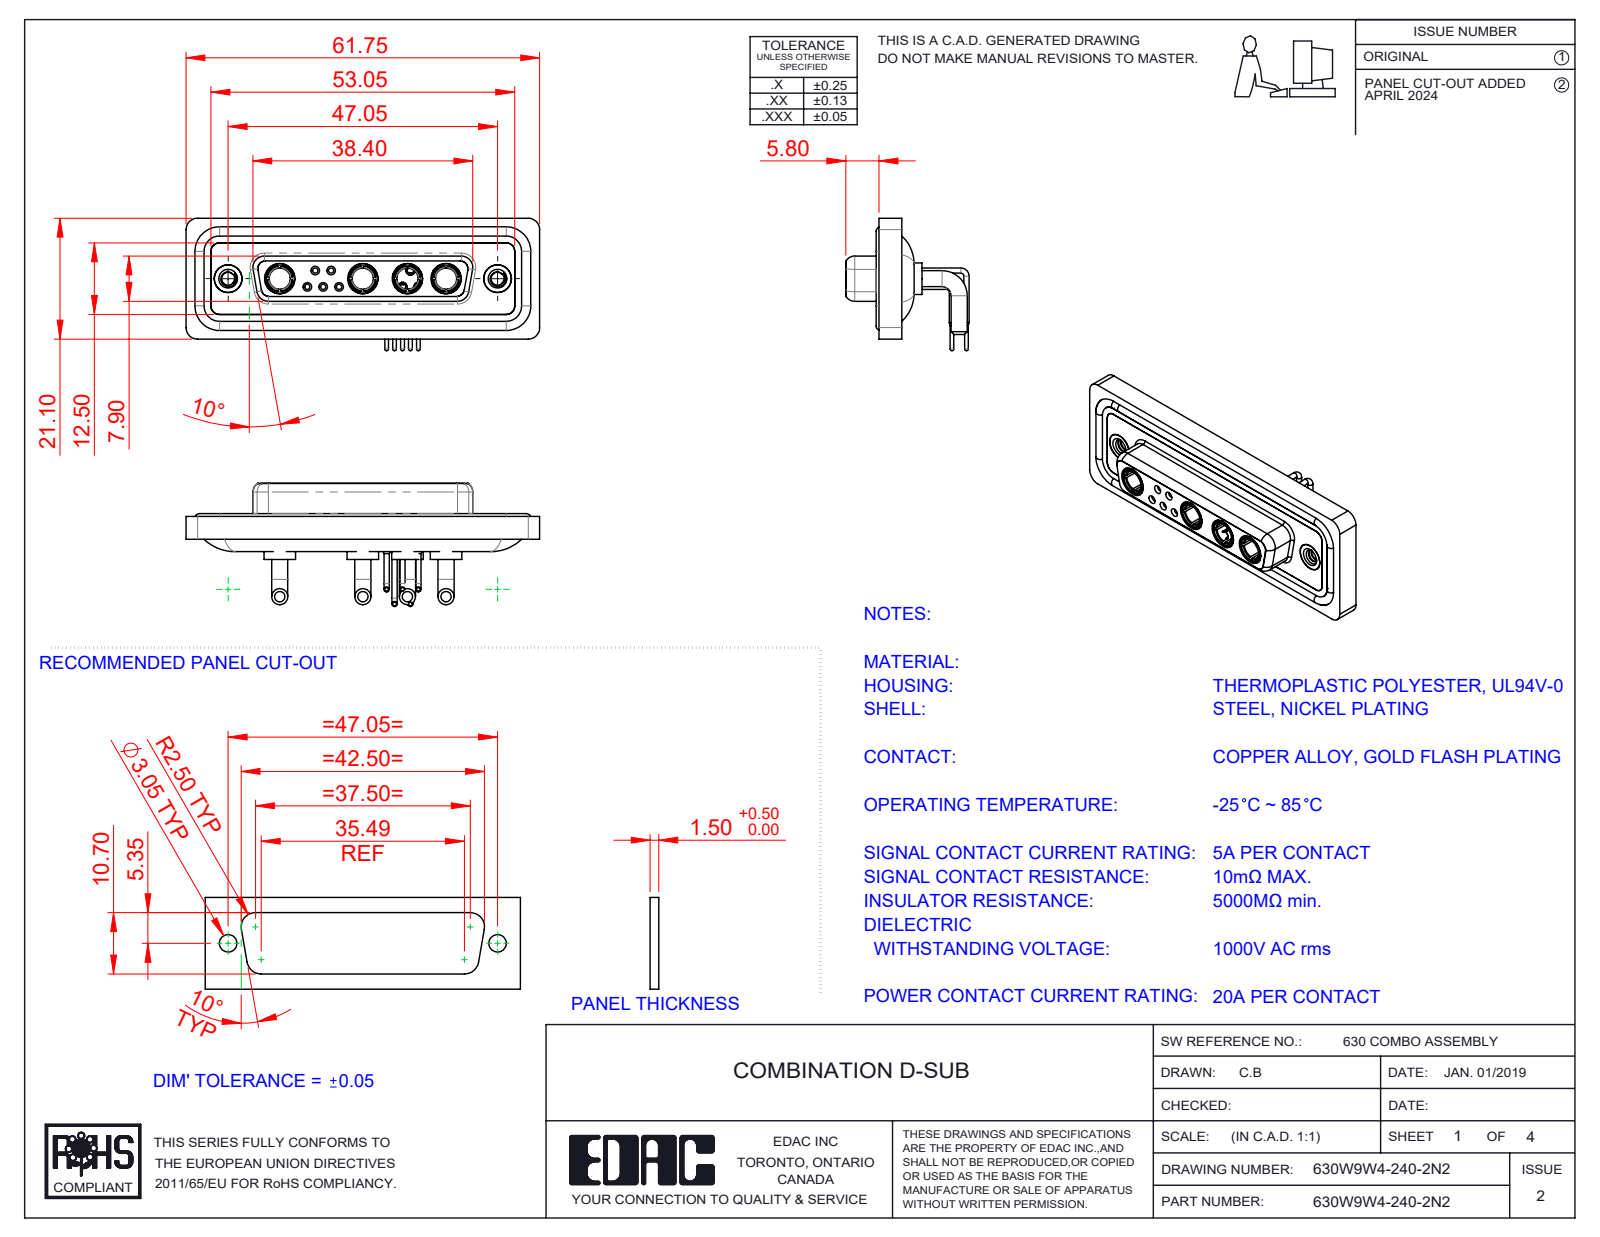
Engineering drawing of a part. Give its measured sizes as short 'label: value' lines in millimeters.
name: 630Combo Housing_9W4; 630Combo Contact Row 2_50 Contacts; 630Combo Shell Rear_25 Contacts; Power Socket_20A RA (+5 more)
written by: SolidWorks 2023 (CONFIG_CONTROL_DESIGN)
unit: mm
bodies: 20 solids, 963 faces (296 planar, 403 cylindrical, 264 other)
size: 61.75 × 23.12 × 21.53
volume: 8 451 mm³; area: 14 047 mm²
holes: 6× ⌀4.85, 5× ⌀0.9, 5× ⌀1.1, 5× ⌀1.5, 5× ⌀2, 4× ⌀3.7, 4× ⌀5.3, 3× ⌀1.6, 2× ⌀1.7, 2× ⌀2.26, 2× ⌀4, 2× ⌀4.05
bosses: 10× ⌀0.9, 9× ⌀1.6, 8× ⌀2.8, 5× ⌀2, 5× ⌀1.5, 5× ⌀0.65, 4× ⌀5.5, 4× ⌀5.2
rounds: 18× R1.5, 18× R2, 8× R1.35, 8× R1.6, 4× R0.25, 4× R0.5, 4× R0.6, 4× R0.65
face distances: 0.4, 1.8, 4.1, 1.1, 1.5, 1.6, 2.5, 3.1, 3.7, 1.4
hole spacings: 3.16, 2.77, 5.04, 13.85, 11.08, 12.79, 15.5, 5.54
